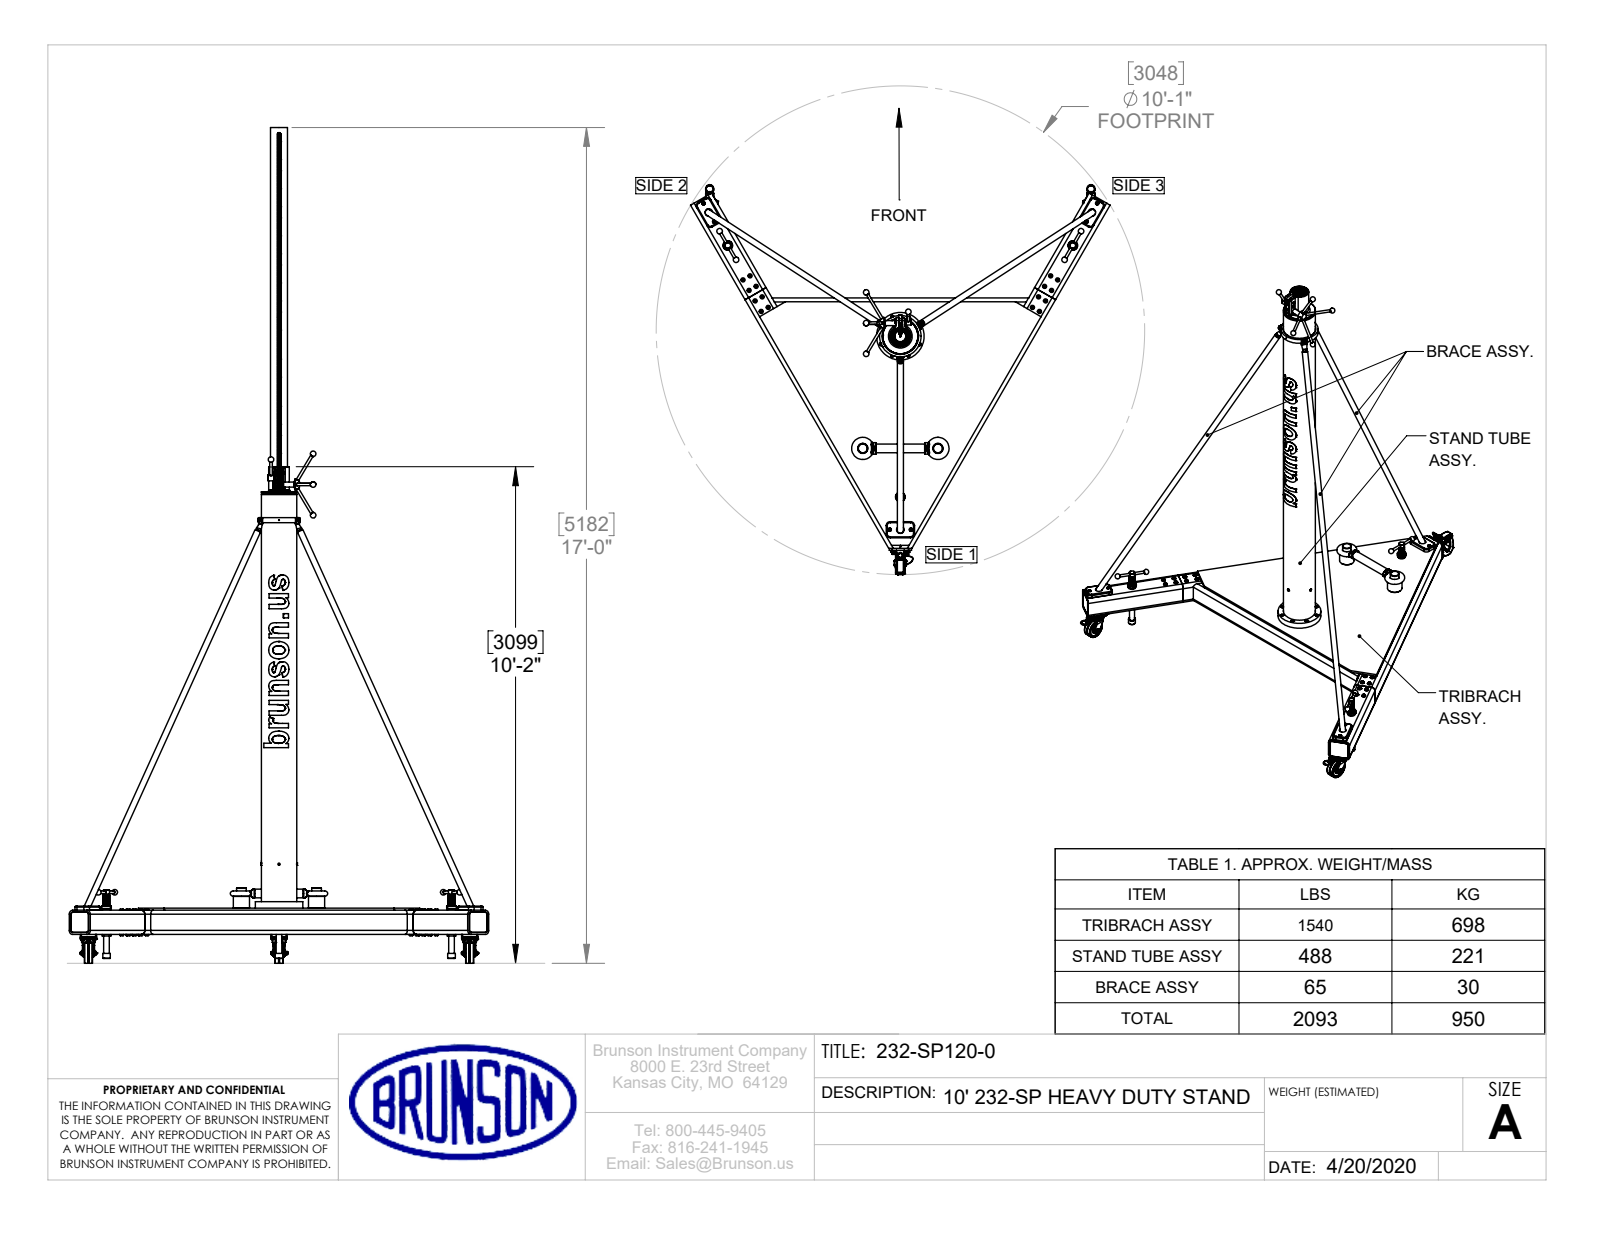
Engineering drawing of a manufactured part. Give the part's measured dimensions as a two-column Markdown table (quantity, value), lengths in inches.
| quantity | value |
| --- | --- |
| part name | 232-SP120-0 |
| STEP written by | SolidWorks 2019 (AUTOMOTIVE_DESIGN) |
| units | inches |
| bodies | 0 solids, 2520 faces (670 planar, 686 cylindrical, 1164 other) |
| overall size | 126.714 × 103.83 × 96.502 |
| round holes (diameter × count) | 0.062 × 3, 0.79 × 3, 1.595 × 3, 1.65 × 3, 0.531 × 2, 2 × 2, 2.5 × 2, 5 × 2, 0.263 × 1, 0.625 × 1, 1.75 × 1, 2.01 × 1 |
| round bosses / shafts (diameter × count) | 1.5 × 9, 0.625 × 6, 2.375 × 5, 4 × 4, 0.625 × 4, 3.386 × 3, 2 × 3, 1.875 × 3 |
| partial cylindrical surfaces (radius × count) | 1 × 39, 0.062 × 33, 0.25 × 31, 0.22 × 24, 0.063 × 19, 0.016 × 18, 0.75 × 16, 0.125 × 13 |
| main face-to-face distances | 6.5, 0.5, 1, 6, 6.001, 6, 0.625, 6.625, 7.125, 47.18 |
| hole center spacings | 25.224, 36.98, 56.627, 60.352, 68.644, 81.065, 85.301, 86.125 |
